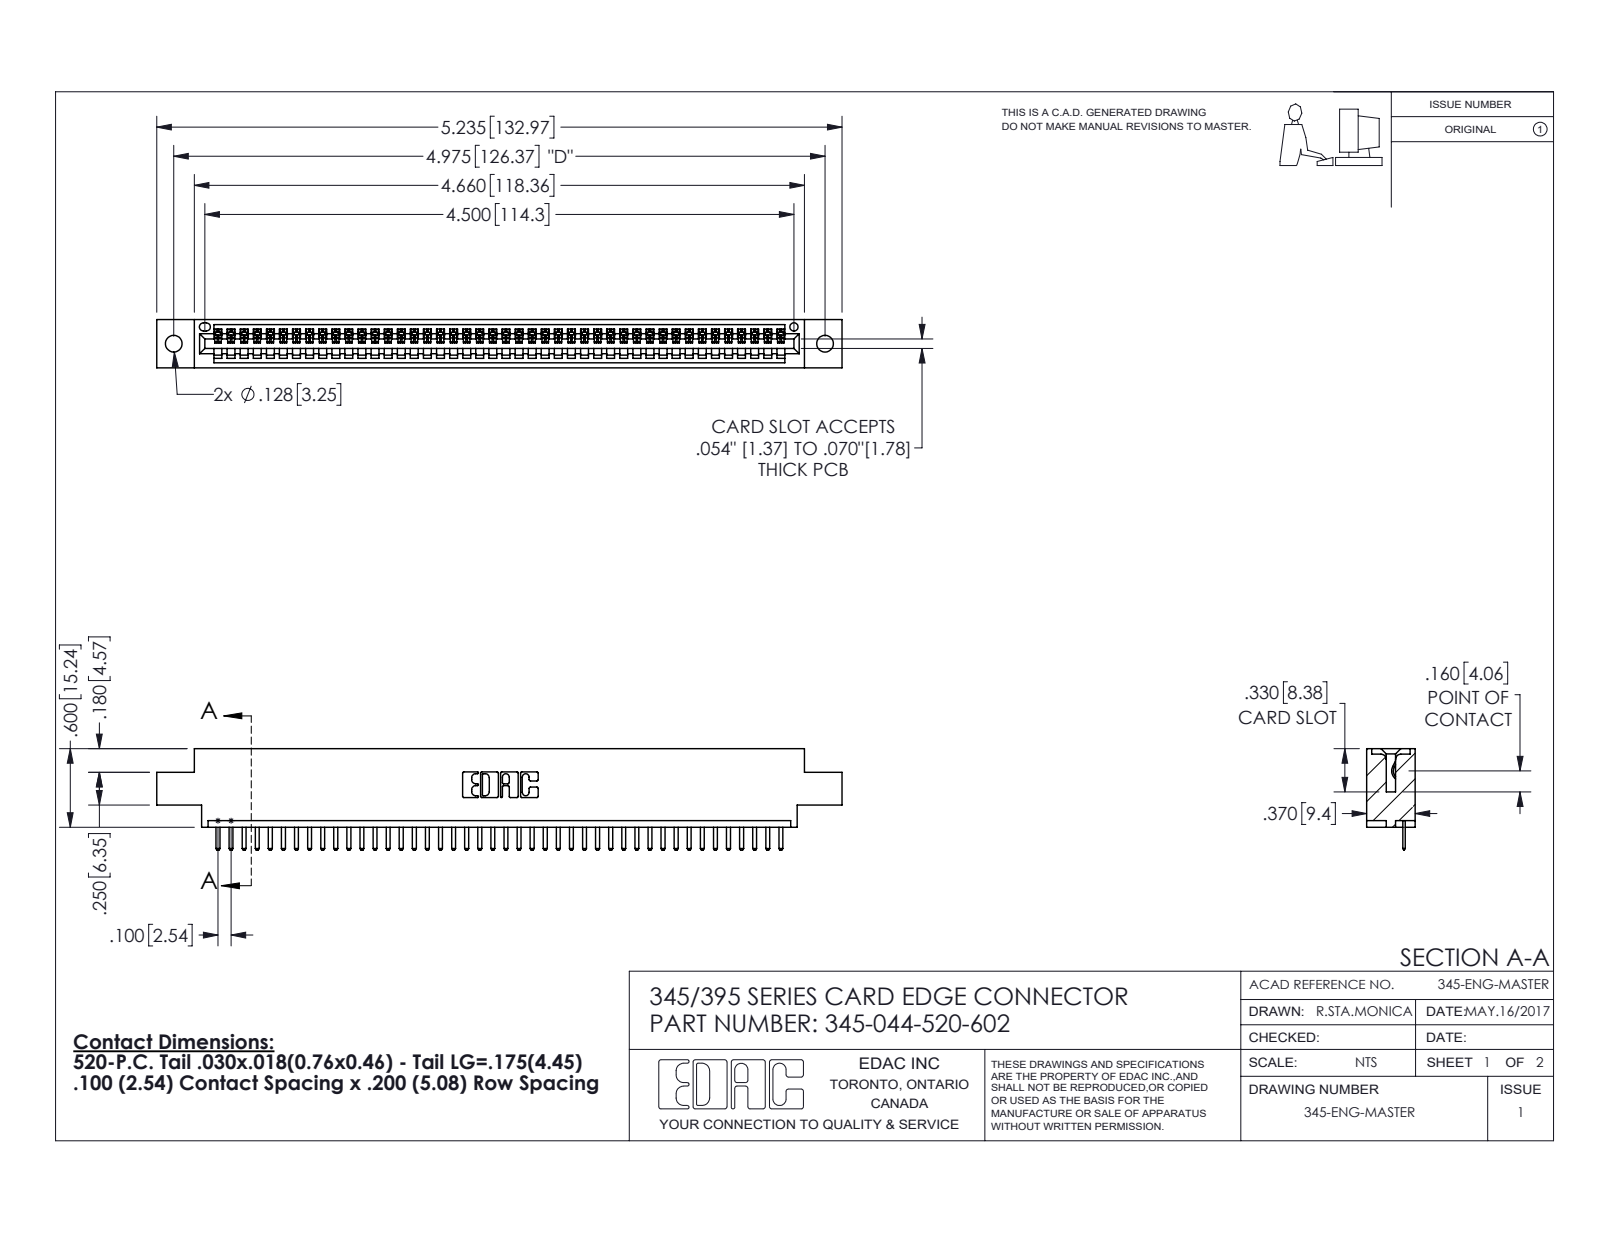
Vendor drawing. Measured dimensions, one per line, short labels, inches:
name: 345-044-520-602; 345-292-001_345-293-120; 345 Part_0.170 Offset - 0.128 Dia
written by: SolidWorks 2016 (CONFIG_CONTROL_DESIGN)
unit: in
bodies: 45 solids, 2858 faces (1932 planar, 926 cylindrical, 0 other)
size: 5.235 × 0.775 × 0.37
volume: 0.755 in³; area: 24.65 in²
holes: 2× ⌀0.128, 1× ⌀0.064
rounds: 90× R0.01, 88× R0.006, 22× R0.01, 6× R0.007, 6× R0.031, 3× R0.026, 2× R0.031, 2× R0.04
face distances: 0.072, 0.298, 0.37, 0.2, 0.098, 0.272, 0.025, 0.225, 0.072, 0.175
hole spacings: 0.27, 4.739, 4.975
